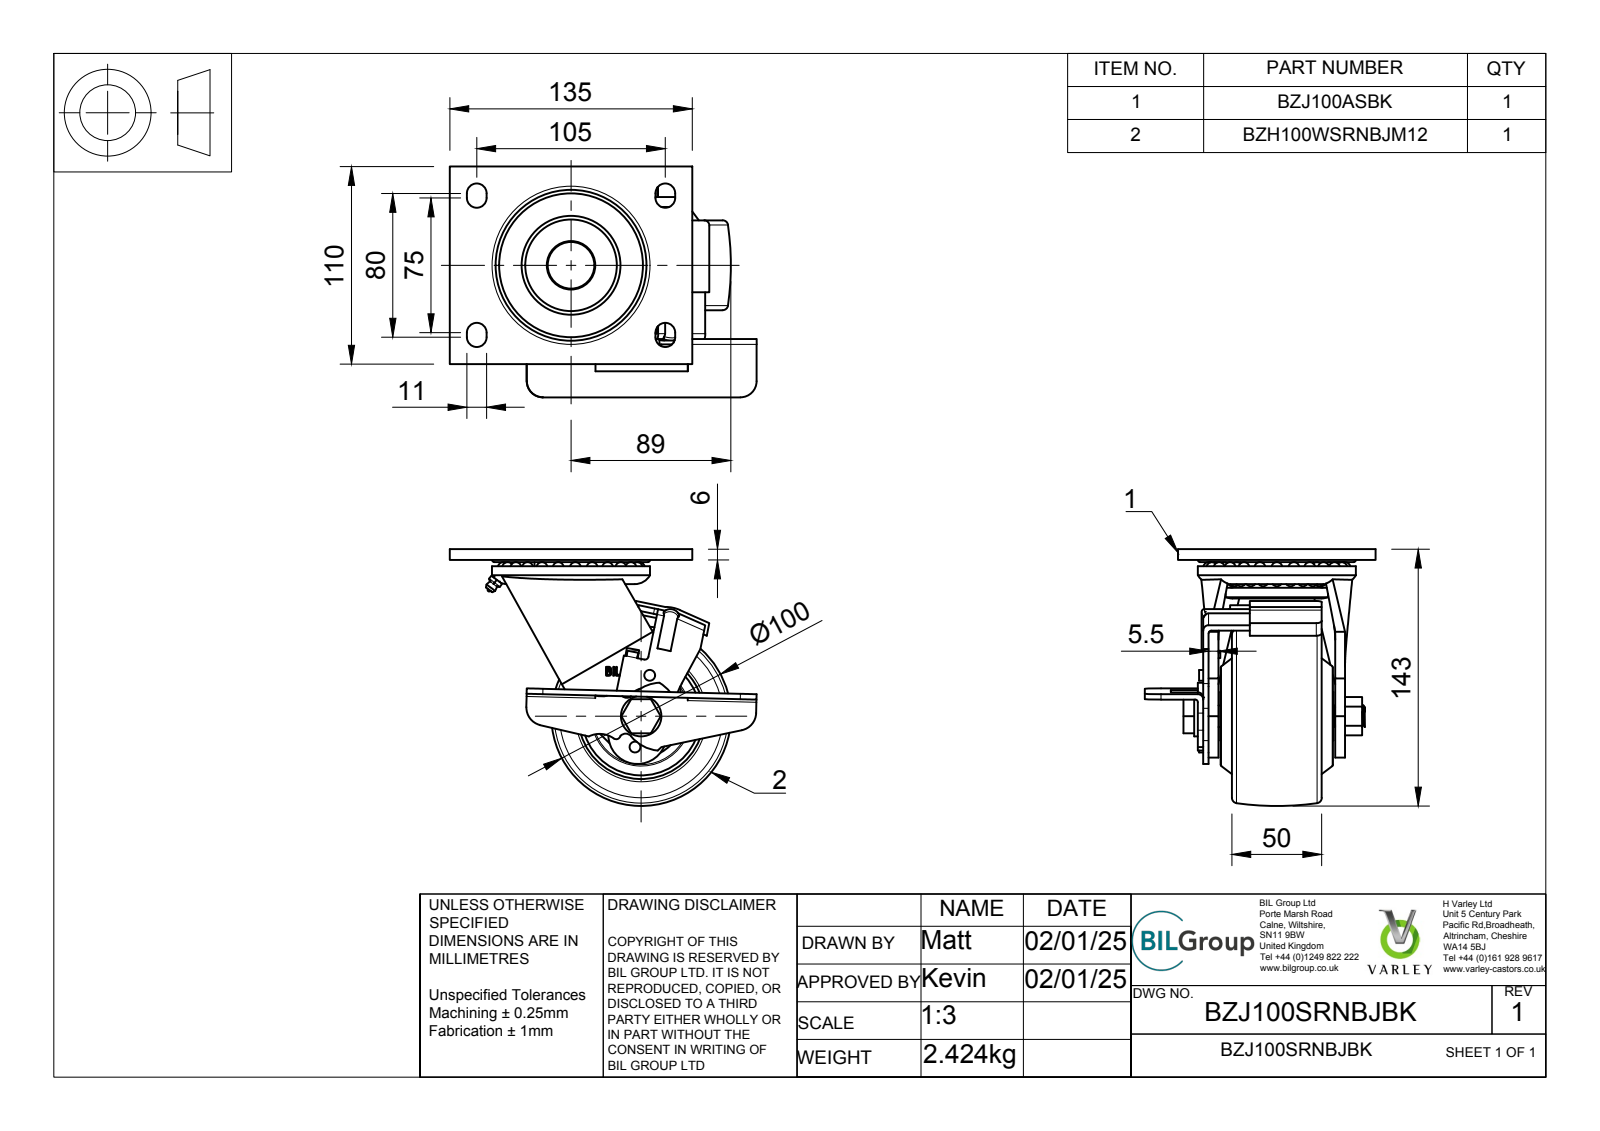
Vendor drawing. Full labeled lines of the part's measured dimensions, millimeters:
Part name (STEP PRODUCT): BZJ100SRNBJBK v3; BZJ100ASBK v1; BZJ100ASBKSLOT; FABRICATED STEEL TOP PLATE (+6 more)
STEP written by: Autodesk Translation Framework v13.20.0.188 (AP242_MANAGED_MODEL_BASED_3D_ENGINEERING_MIM_LF)
Units: millimetres
Bodies: 84 solids, 1121 faces (486 planar, 171 cylindrical, 464 other)
Overall size (bounding box): 170.83 × 143 × 128.5
Volume: 613 113 mm³ · Surface area: 231 844 mm²
Round holes (diameter × count): ⌀12 ×1, ⌀12.5 ×1, ⌀13 ×1, ⌀15 ×1, ⌀17 ×1, ⌀20 ×1, ⌀28.5 ×1, ⌀30.8 ×1, ⌀40.3 ×1, ⌀40.5 ×1, ⌀40.9 ×1, ⌀42 ×1
Round bosses / shafts (diameter × count): ⌀6 ×2, ⌀88 ×1, ⌀69 ×1, ⌀57 ×1, ⌀47 ×1, ⌀40.8 ×1, ⌀40.62 ×1, ⌀31.3 ×1
Partial cylindrical surfaces — rounded edges, fillets, slot ends (radius × count): R5.5 ×8, R3 ×6, R1.5 ×4, R2 ×2, R2.45 ×2, R3.96 ×2, R8.5 ×2, R9 ×2
Main face-to-face distances: 3, 6, 8.5, 1.25, 63, 70.5, 5.5, 11.5, 13, 7.25
